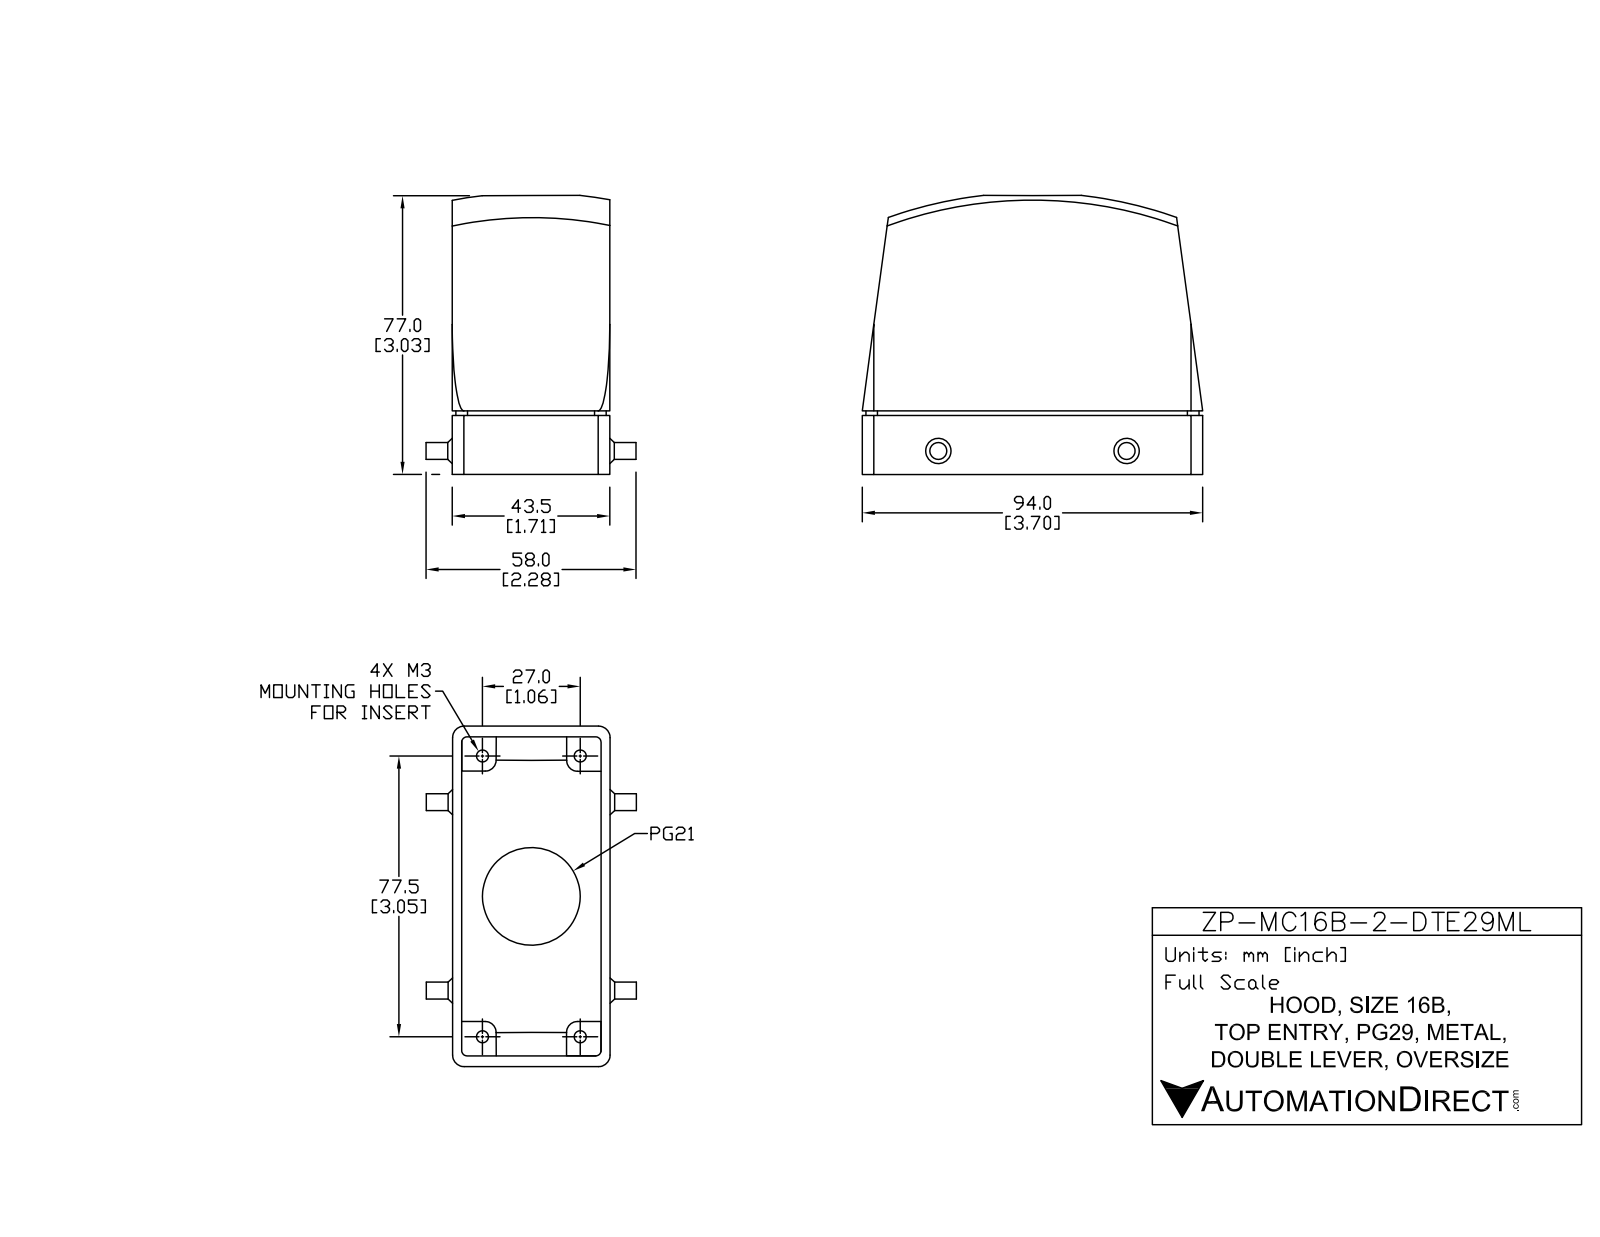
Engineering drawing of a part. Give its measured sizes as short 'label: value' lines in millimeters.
name: ZP-MC16B-2-DTE29ML
written by: SolidWorks 2011 (AUTOMOTIVE_DESIGN)
unit: mm
bodies: 9 solids, 98 faces (58 planar, 30 cylindrical, 10 other)
size: 94 × 76.31 × 58
volume: 66 483 mm³; area: 51 202 mm²
holes: 4× ⌀3.5, 1× ⌀35
bosses: 2× ⌀4.67
rounds: 8× R3.2, 4× R1.5, 4× R3, 1× R0.7
face distances: 2.5, 41, 43.5, 38.5, 9.5, 2.96, 91.04, 78.58, 81.54, 12.46
hole spacings: 42.31, 28.96, 79.5, 84.61
